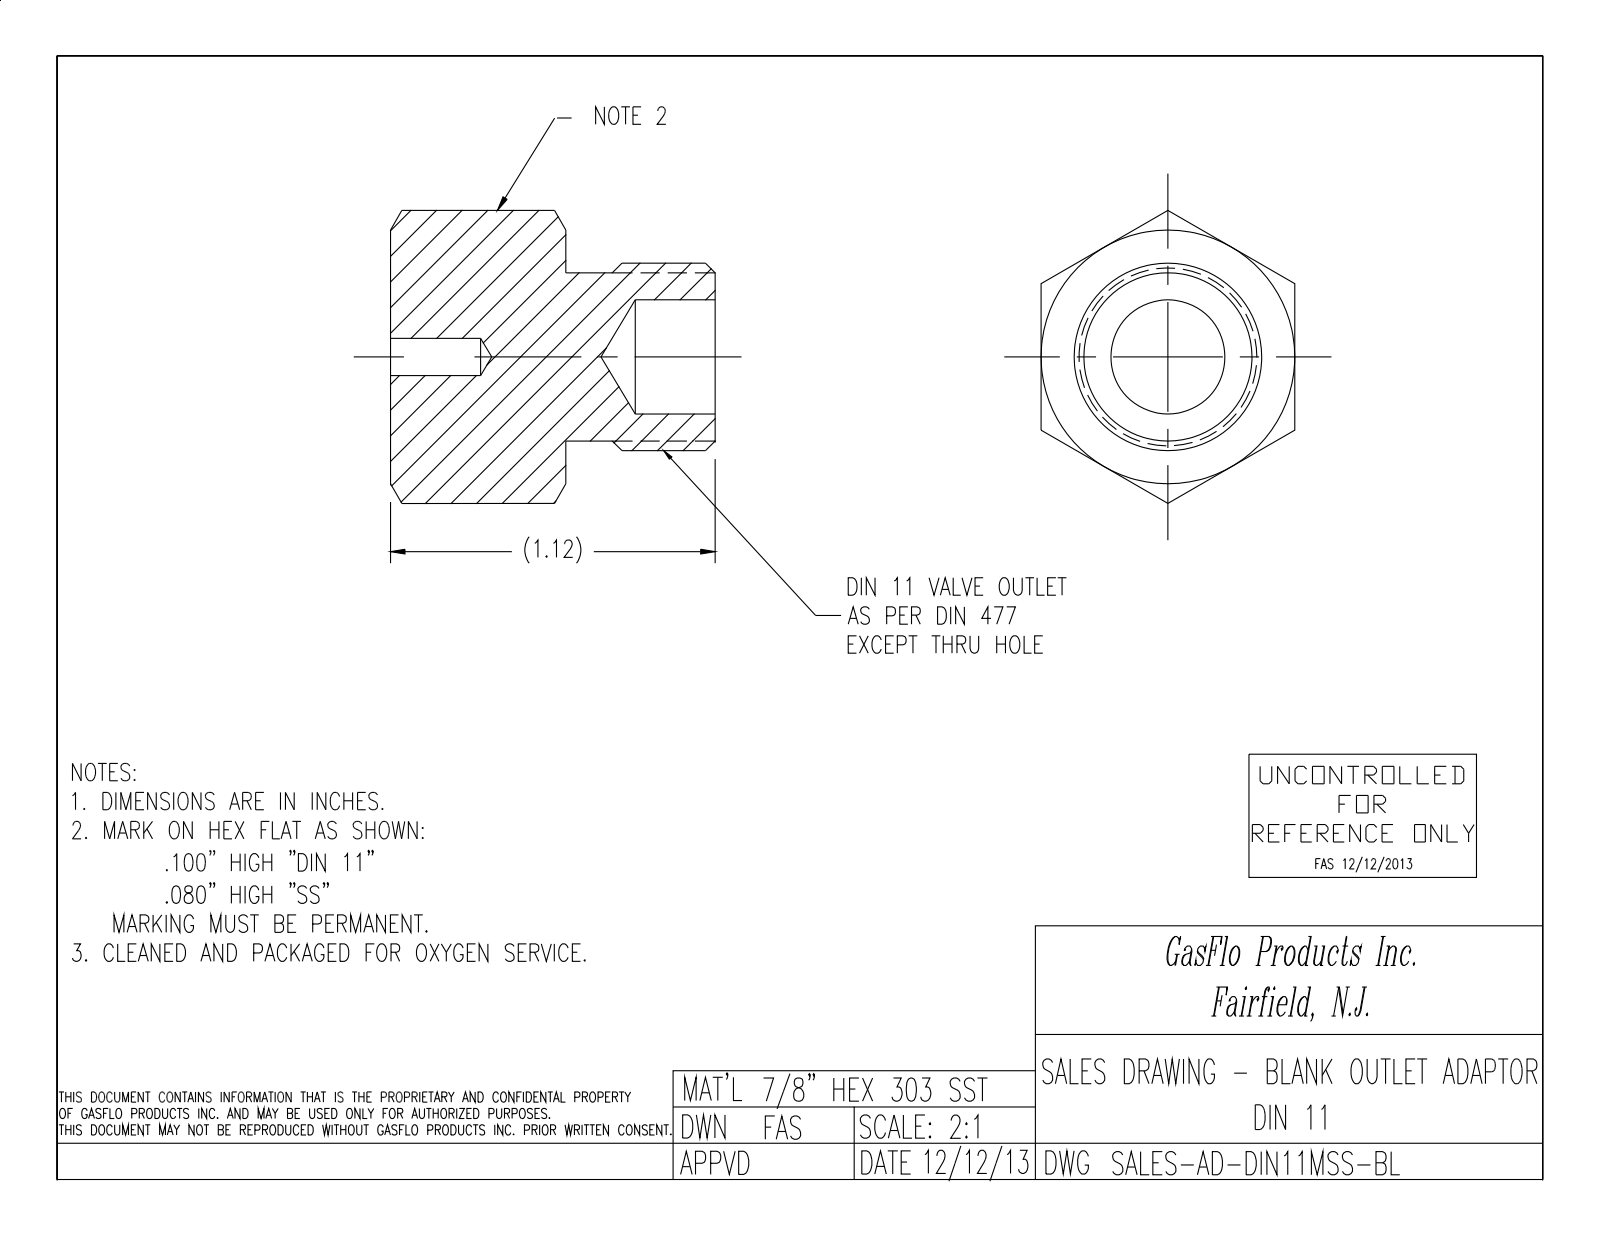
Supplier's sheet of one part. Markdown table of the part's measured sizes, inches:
| quantity | value |
| --- | --- |
| part name | AD-DIN11MSS-BL |
| STEP written by | SolidWorks 2018 (CONFIG_CONTROL_DESIGN) |
| units | inches |
| bodies | 1 solid, 130 faces (53 planar, 18 cylindrical, 59 other) |
| overall size | 1.12 × 1.01 × 0.875 |
| volume | 0.506 in³ |
| surface area | 5.102 in² |
| round holes (diameter × count) | 0.129 × 1, 0.394 × 1 |
| round bosses / shafts (diameter × count) | 0.651 × 1, 0.58 × 1 |
| main face-to-face distances | 0.875, 0.605, 1.12, 0.515, 0.87, 0.097, 0.104, 0.053, 0.104, 0.164 |
